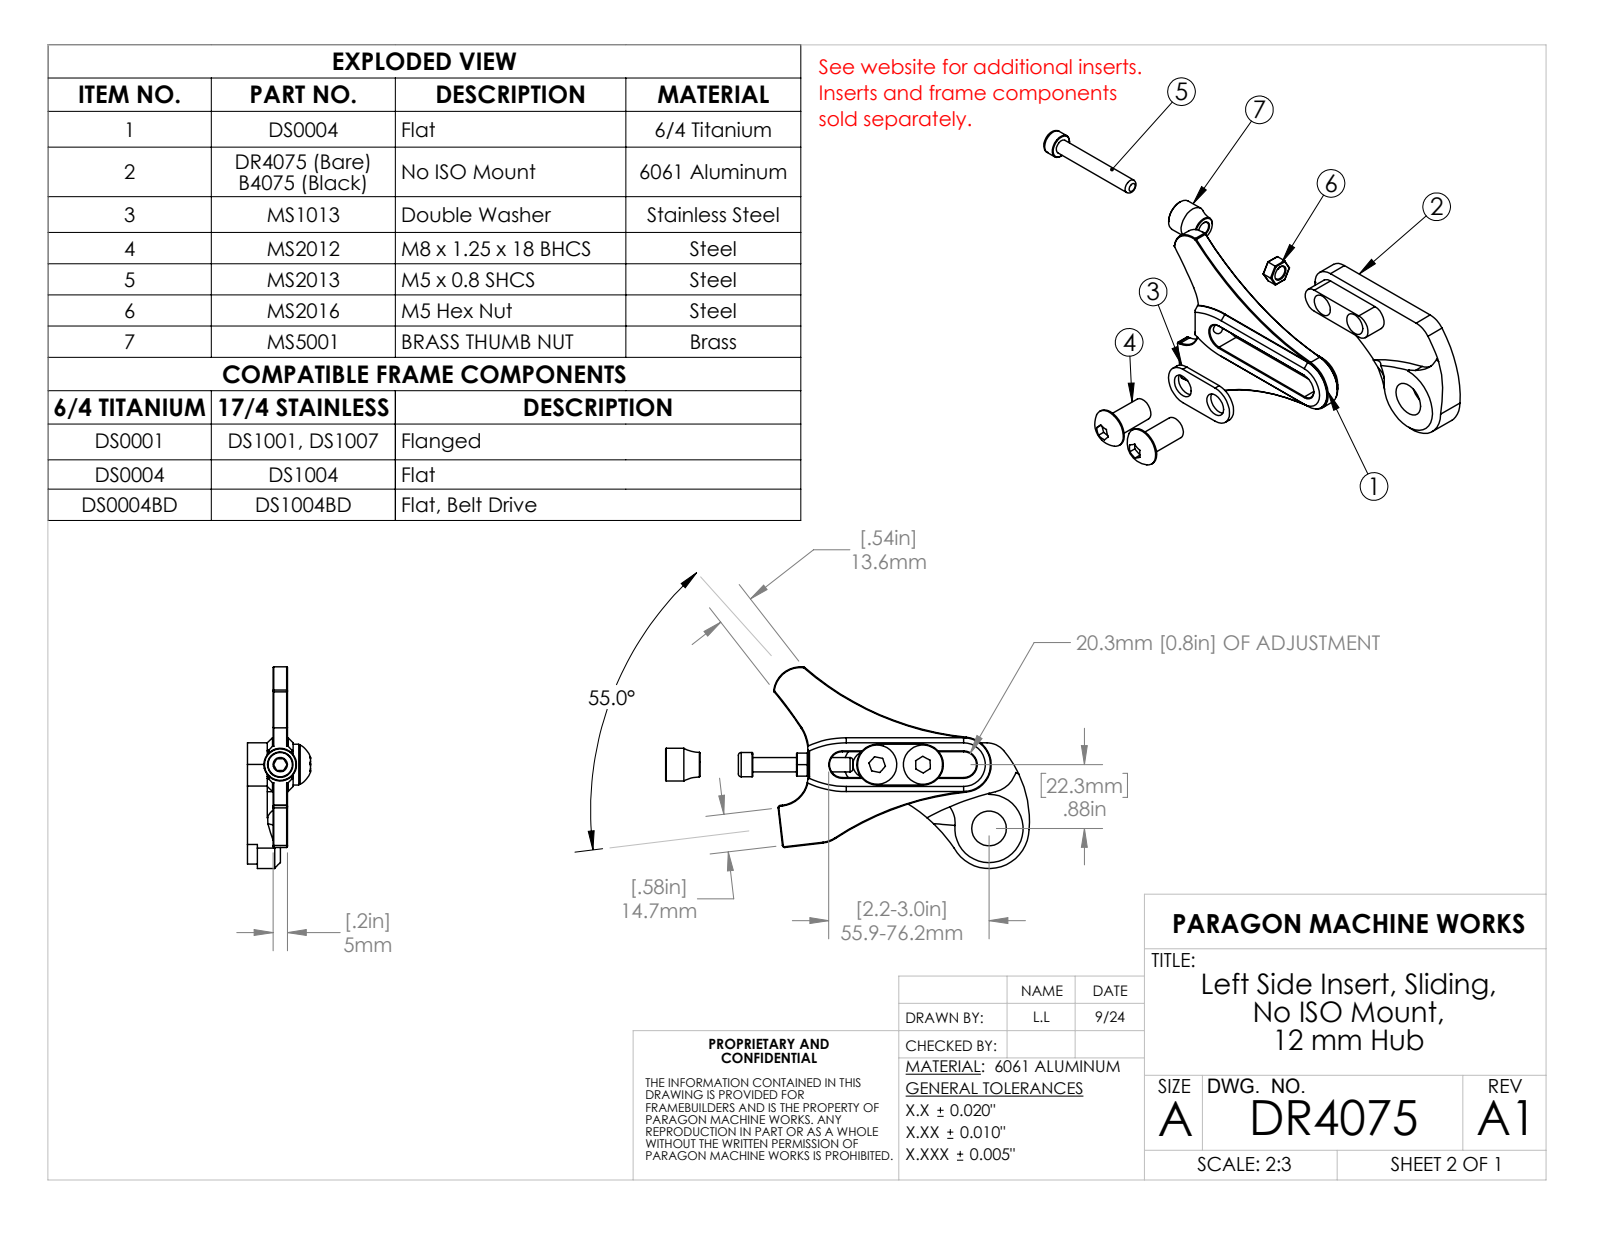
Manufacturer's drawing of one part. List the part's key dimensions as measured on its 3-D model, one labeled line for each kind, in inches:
Part name (STEP PRODUCT): DR4075; MS5001; MS2012; MS2013 (+4 more)
STEP written by: SolidWorks 2023 (AUTOMOTIVE_DESIGN)
Units: inches
Bodies: 8 solids, 248 faces (86 planar, 86 cylindrical, 76 other)
Overall size (bounding box): 7.502 × 4.868 × 2.774
Volume: 1.832 in³ · Surface area: 26.54 in²
Round holes (diameter × count): ⌀0.197 ×2, ⌀0.312 ×2, ⌀0.327 ×2, ⌀0.335 ×1, ⌀0.477 ×1
Round bosses / shafts (diameter × count): ⌀0.539 ×2, ⌀0.315 ×2, ⌀0.449 ×1
Partial cylindrical surfaces — rounded edges, fillets, slot ends (radius × count): R0.01 ×12, R0.03 ×4, R0.178 ×4, R0.28 ×2, R0.3 ×2, R0.4 ×2, R1.27 ×2, R4 ×2
Main face-to-face distances: 0.197, 2.05, 1.853, 0.079, 0.274, 1.579, 1.776, 0.276, 1.448, 1.172
Hole centre spacings: 0.63, 1.262, 1.5, 1.77
